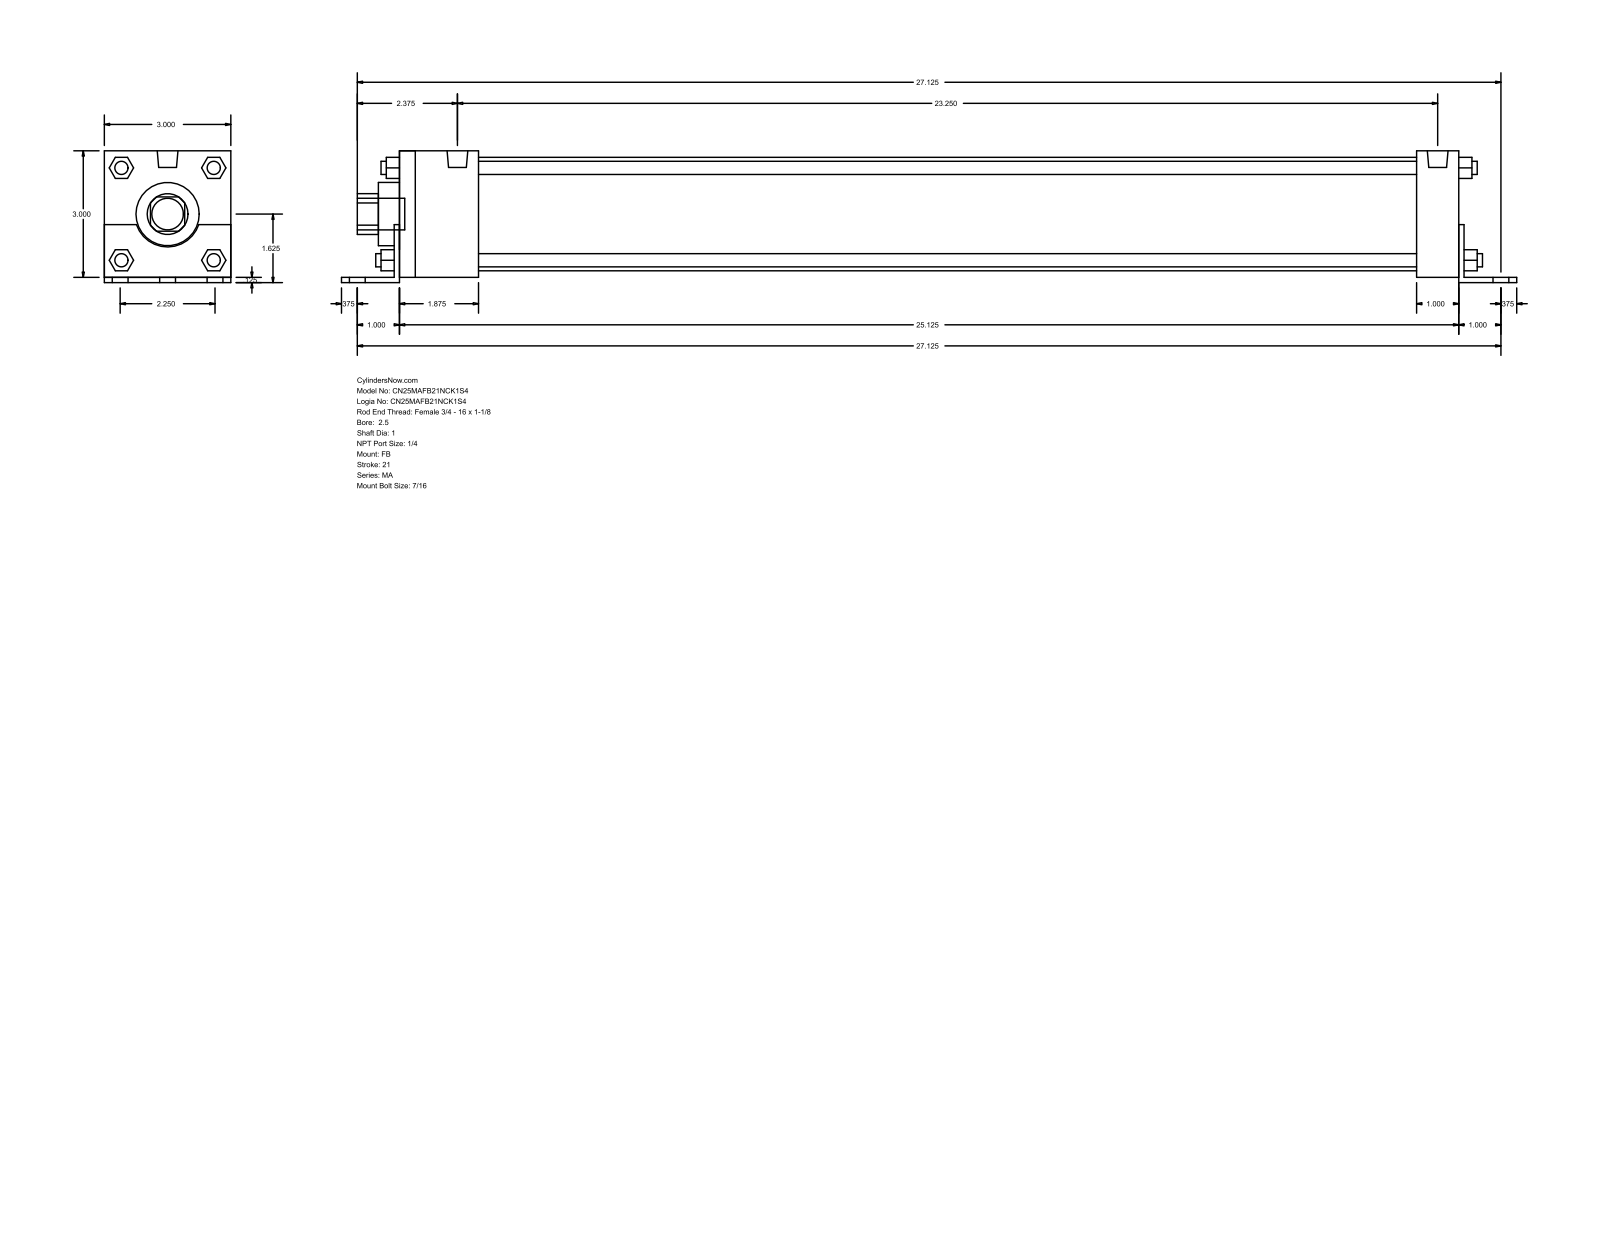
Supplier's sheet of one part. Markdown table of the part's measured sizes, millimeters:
| quantity | value |
| --- | --- |
| part name | MA_FB__0250_1 |
| STEP written by | GSSL Pune (CONFIG_CONTROL_DESIGN) |
| units | millimeters |
| bodies | 0 solids, 140 faces (105 planar, 35 cylindrical, 0 other) |
| overall size | 708.02 × 79.38 × 76.2 |
| round holes (diameter × count) | 25.4 × 1, 38.1 × 1, 68.33 × 1 |
| round bosses / shafts (diameter × count) | 7.94 × 8, 11.11 × 6, 12.49 × 2, 19.05 × 1 |
| partial cylindrical surfaces (radius × count) | 12.29 × 1, 19.81 × 1 |
| main face-to-face distances | 76.2, 3.17, 79.37, 641.35, 638.18, 12.7, 47.63, 590.55, 593.72, 612.77 |
